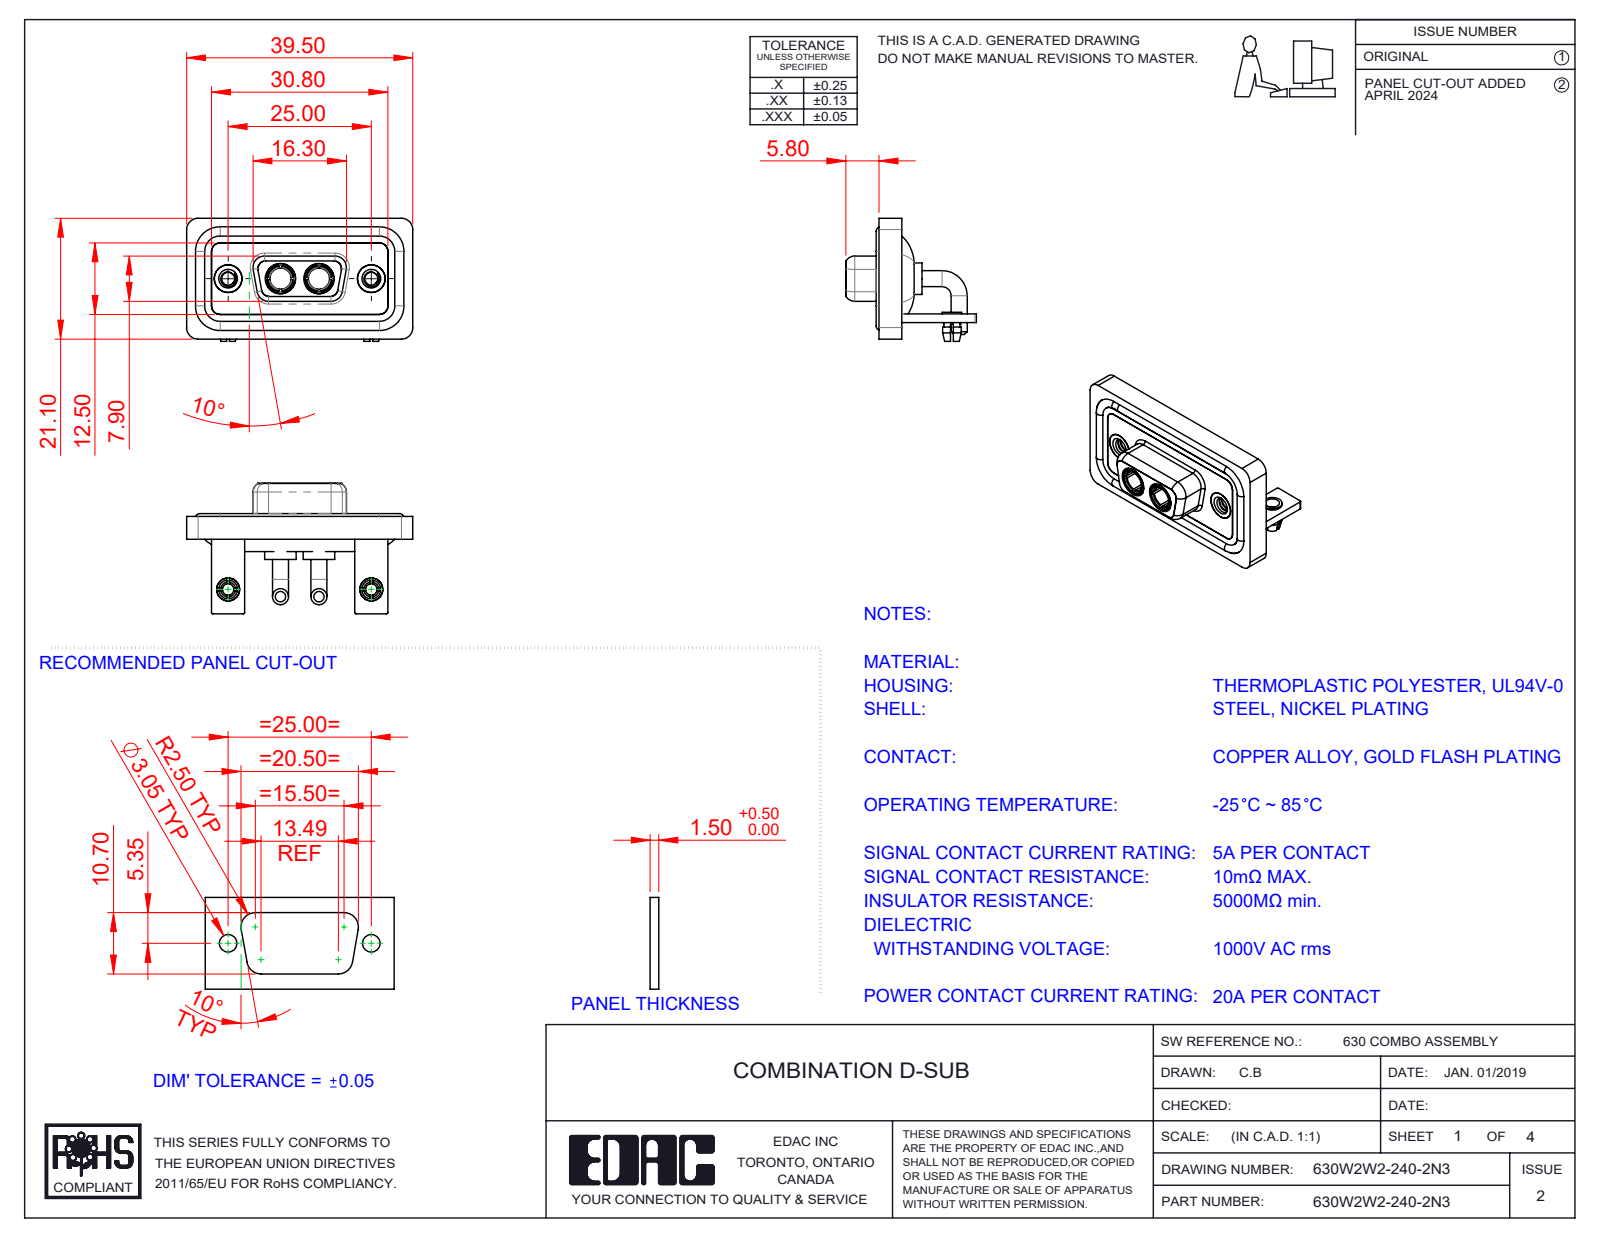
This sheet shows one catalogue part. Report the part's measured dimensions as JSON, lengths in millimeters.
{"part_name": "630Combo Board Lock_50 Contacts; 630Combo Threaded Rivet_2; 630Combo Waterproof Housing_09 Contacts; 630Combo Housing_2W2 (+5 more)", "step_written_by": "SolidWorks 2023 (CONFIG_CONTROL_DESIGN)", "units": "millimeters", "bodies": {"solids": 15, "faces": 682, "planar": 231, "cylindrical": 294, "other": 157}, "overall_size": [39.5, 22.8, 21.5], "volume_mm3": 5219, "surface_area_mm2": 8732, "round_holes": [[4.85, 4], [2, 2], [2.26, 2], [2.5, 2], [3.2, 2], [3.7, 2], [4, 2], [4.05, 2], [5, 2], [5.3, 2]], "round_bosses_or_shafts": [[2.8, 4], [1.6, 4], [5.5, 2], [5.2, 2], [4.96, 2], [4.95, 2], [4.8, 2], [4.75, 2]], "partial_cylinders_radius": [[2, 19], [1.5, 18], [0.25, 16], [1.35, 8], [1.6, 8], [0.5, 5], [0.6, 4], [0.65, 4]], "face_to_face_distances": [0.4, 2.9, 1.5, 1.8, 1.1, 3.7, 0.8, 2.5, 1.6, 3.1], "hole_center_spacings": [9.14, 15.86, 25, 6.72]}
